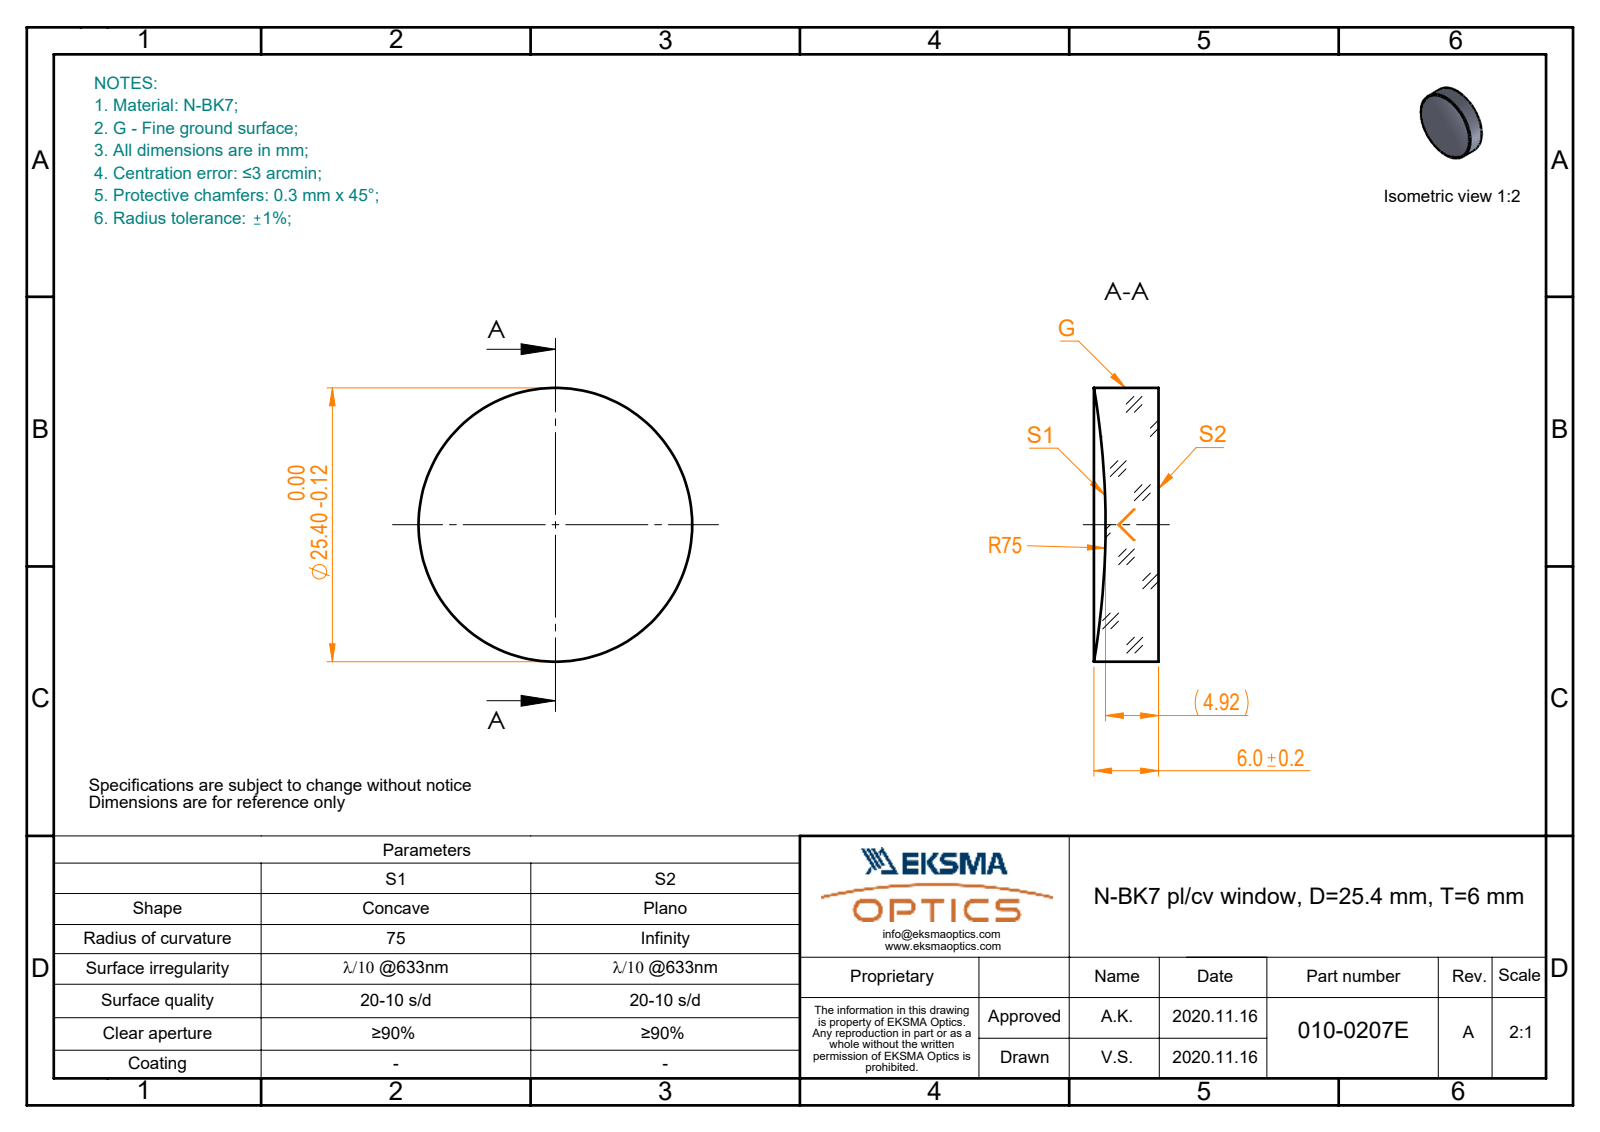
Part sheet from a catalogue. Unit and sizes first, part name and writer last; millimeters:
Units: millimetres
Overall size (bounding box): 25.4 × 25.4 × 6
Round bosses / shafts (diameter × count): ⌀25.4 ×1
Volume: 2 765 mm³ · Surface area: 1 496 mm²
Bodies: 1 solid, 5 faces (1 planar, 2 cylindrical, 2 other)
Part name (STEP PRODUCT): 010-0207E_N-BK7_PCV_mirror
STEP written by: SolidWorks 2019 (CONFIG_CONTROL_DESIGN)
